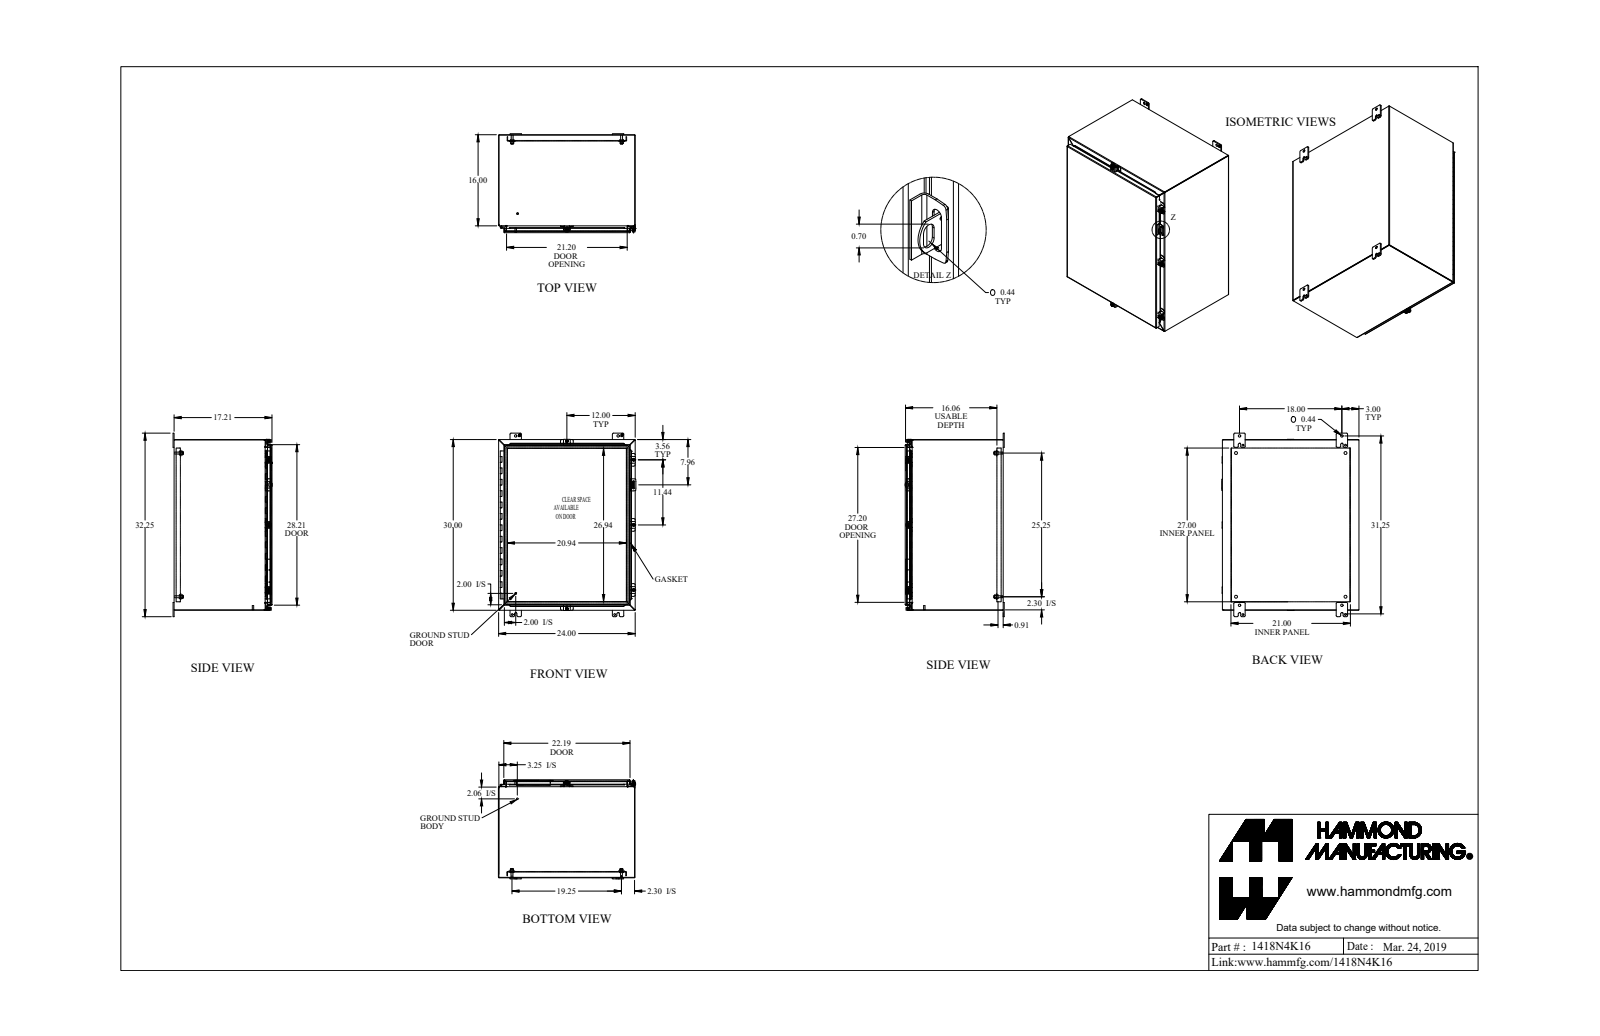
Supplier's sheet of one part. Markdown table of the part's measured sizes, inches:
| quantity | value |
| --- | --- |
| part name | 1418N4K16_Default |
| STEP written by | SolidWorks 2019 (CONFIG_CONTROL_DESIGN) |
| units | inches |
| bodies | 45 solids, 1595 faces (949 planar, 552 cylindrical, 94 other) |
| overall size | 32.25 × 24.126 × 17.437 |
| volume | 321.1 in³ |
| surface area | 8 502 in² |
| round holes (diameter × count) | 0.213 × 5, 0.265 × 5, 0.375 × 5, 0.313 × 4, 0.437 × 4, 0.5 × 4, 0.307 × 2, 0.445 × 2, 0.125 × 1, 0.187 × 1 |
| round bosses / shafts (diameter × count) | 0.5 × 5, 0.39 × 5, 0.244 × 5, 0.65 × 4, 0.375 × 4, 0.33 × 4, 1 × 2, 0.281 × 2 |
| partial cylindrical surfaces (radius × count) | 0.25 × 28, 0.048 × 27, 0.143 × 27, 0.188 × 26, 0.036 × 22, 0.108 × 22, 0.125 × 10, 0.141 × 10 |
| main face-to-face distances | 0.072, 23.928, 29.928, 0.072, 17.066, 17.138, 17.138, 17.21, 0.095, 16.106 |
| hole center spacings | 29.018, 31.751, 9.857, 18, 19.25, 1.736, 3.065, 9.857 |
